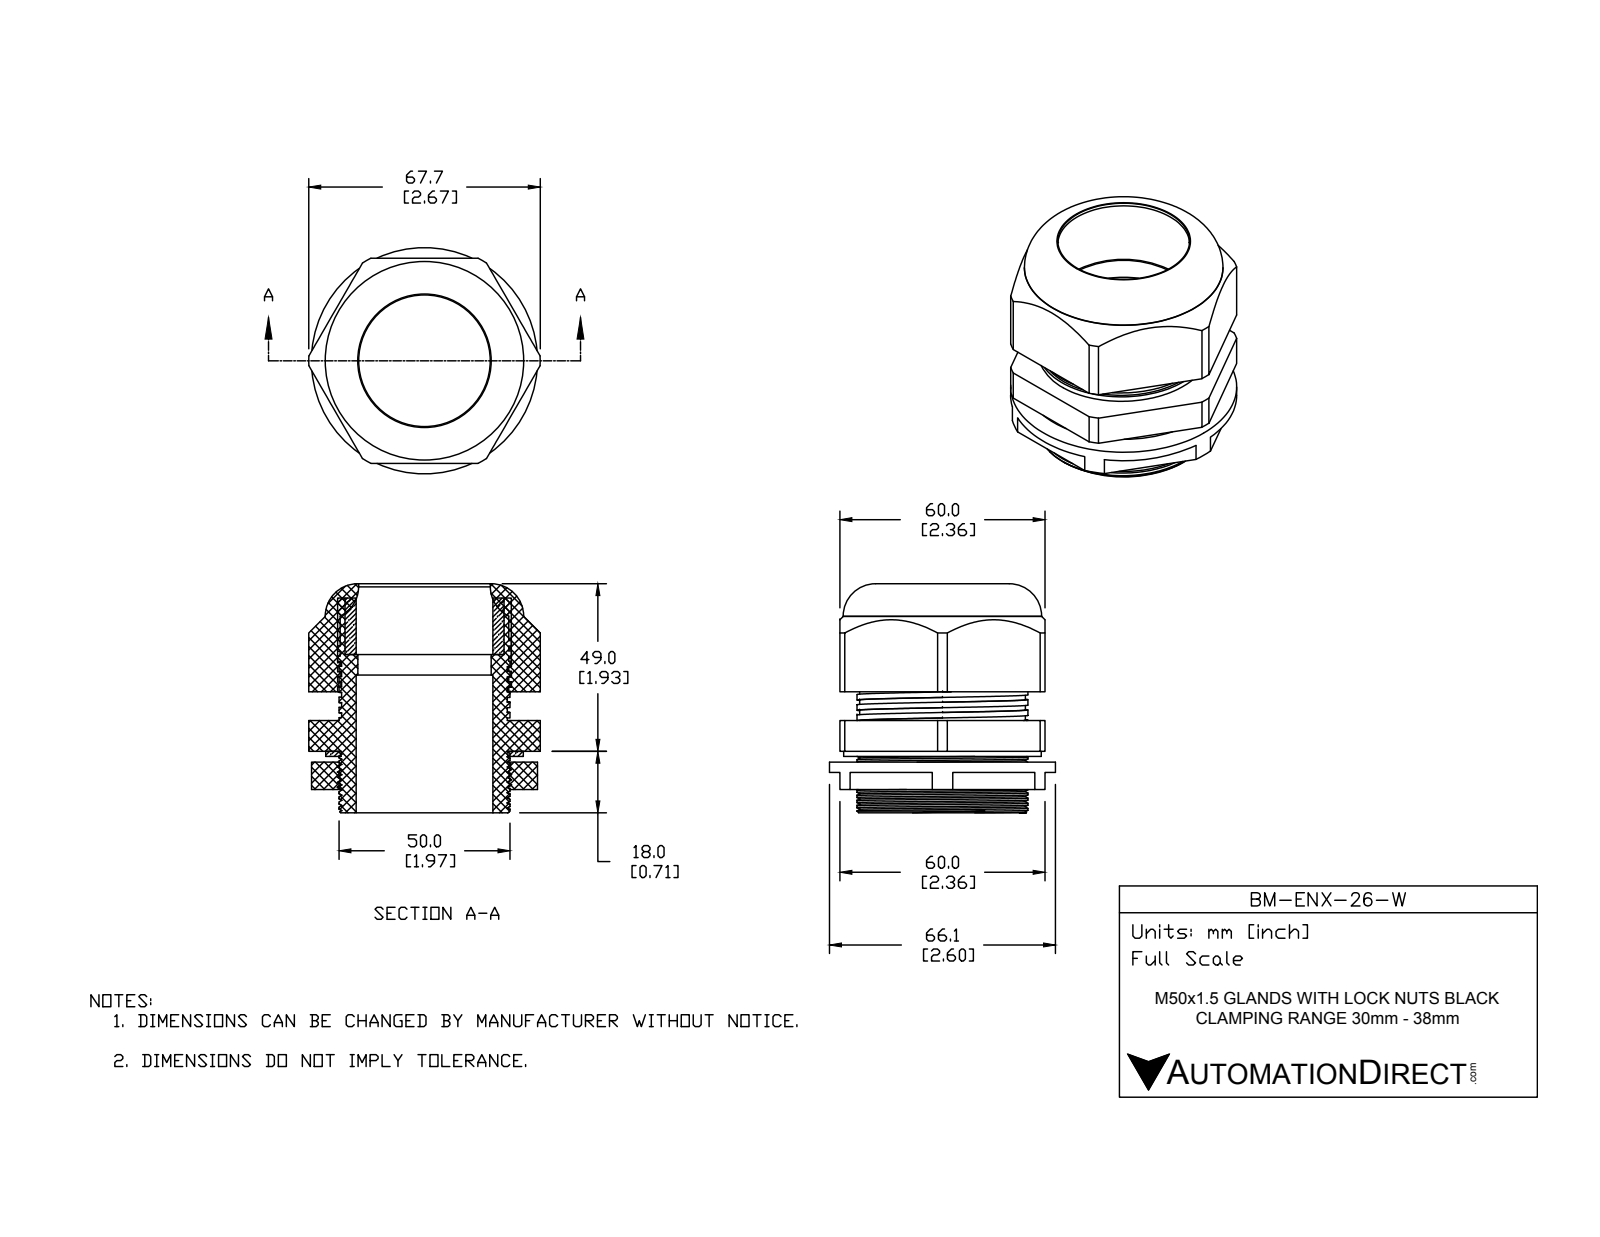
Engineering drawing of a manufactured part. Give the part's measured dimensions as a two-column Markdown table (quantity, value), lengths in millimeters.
| quantity | value |
| --- | --- |
| part name | BM-ENX-26-W |
| STEP written by | SolidWorks 2015 (CONFIG_CONTROL_DESIGN) |
| units | millimeters |
| bodies | 5 solids, 257 faces (140 planar, 98 cylindrical, 19 other) |
| overall size | 67.7 × 67 × 66.1 |
| volume | 99 233 mm³ |
| surface area | 55 544 mm² |
| round holes (diameter × count) | 38.5 × 1, 39 × 1, 40 × 1, 46.5 × 1, 48.8 × 1, 49.33 × 1 |
| round bosses / shafts (diameter × count) | 66.1 × 1, 58.06 × 1, 57.8 × 1, 50.8 × 1, 50 × 1 |
| partial cylindrical surfaces (radius × count) | 33.85 × 1 |
| main face-to-face distances | 60, 9, 10.5, 2.5, 16.5, 46.3, 11.5, 8, 19.5, 27.9 |
